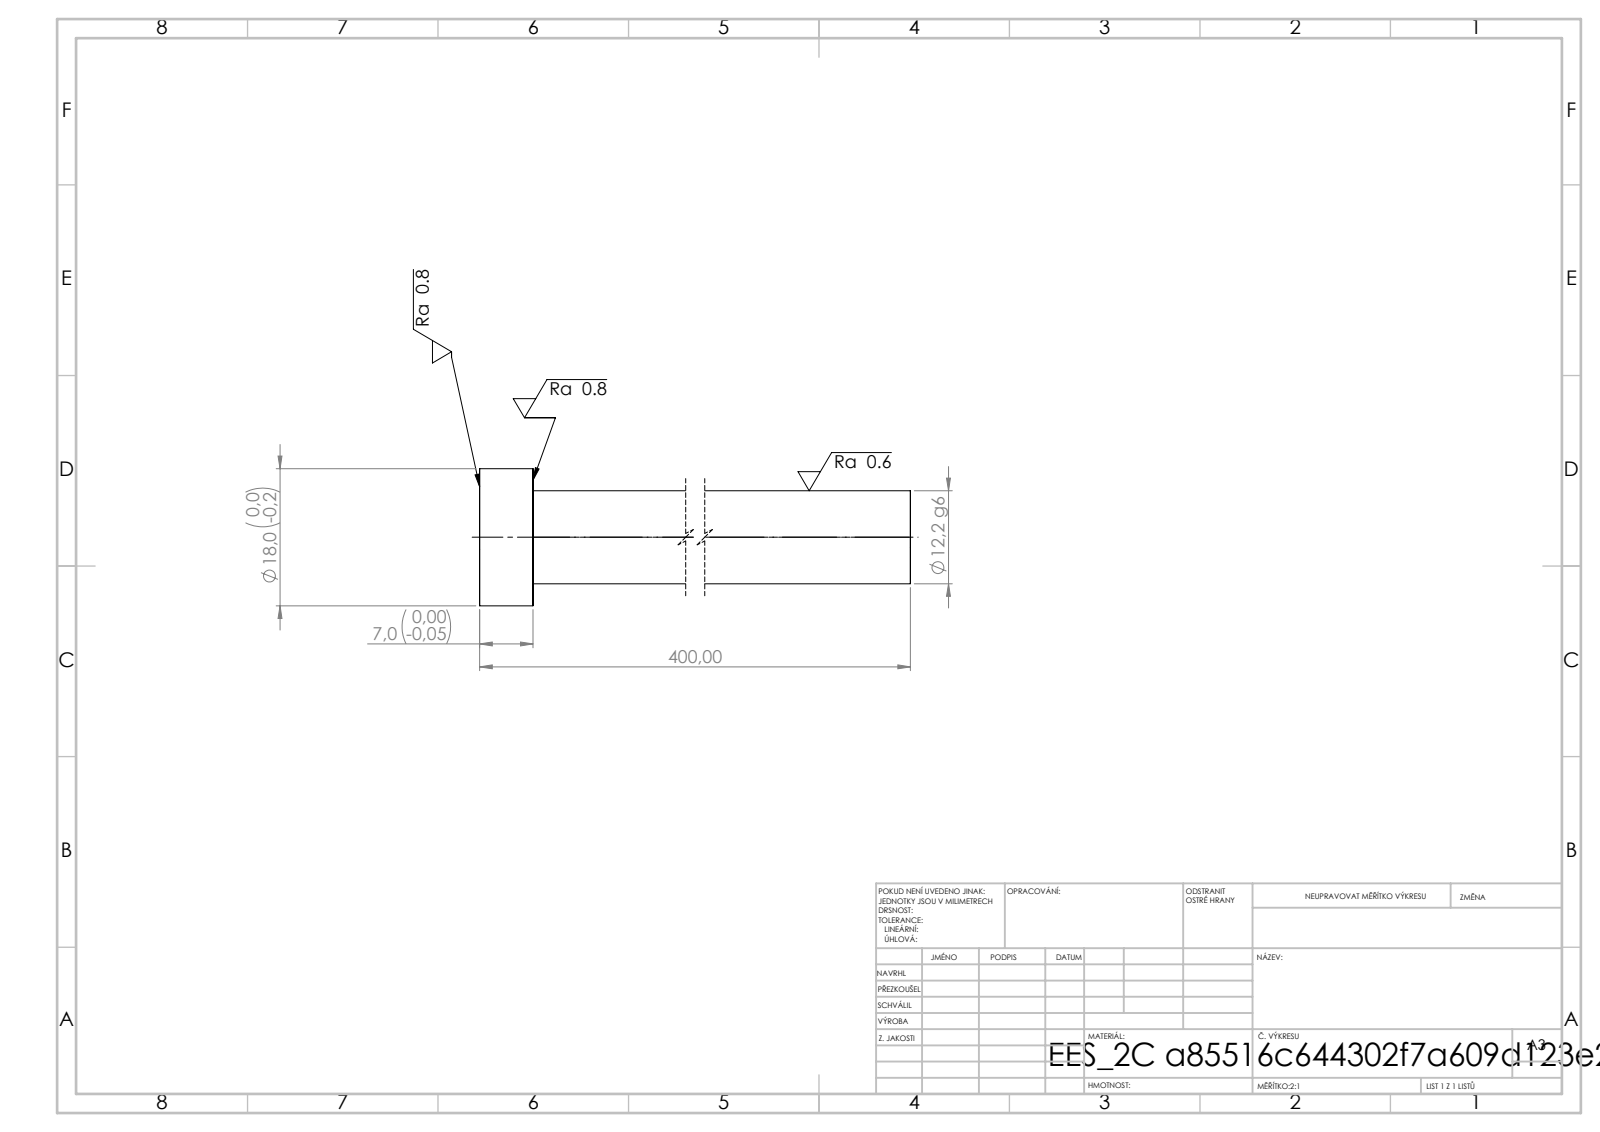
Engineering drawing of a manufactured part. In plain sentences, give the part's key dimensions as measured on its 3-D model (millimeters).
Its 3-D file was written by "SolidWorks 2019 (CONFIG_CONTROL_DESIGN)". It is 1 solid with 7 faces: 3 planar, 4 cylindrical and 0 other. Overall it measures 400 by 18 by 18 millimeters. Its volume is 47 722 cubic millimeters and its surface area 15 967 square millimeters. Round bosses or shafts: 1 of diameter 18, 1 of diameter 12.2. The main face-to-face distances are 7, 400, 393.
